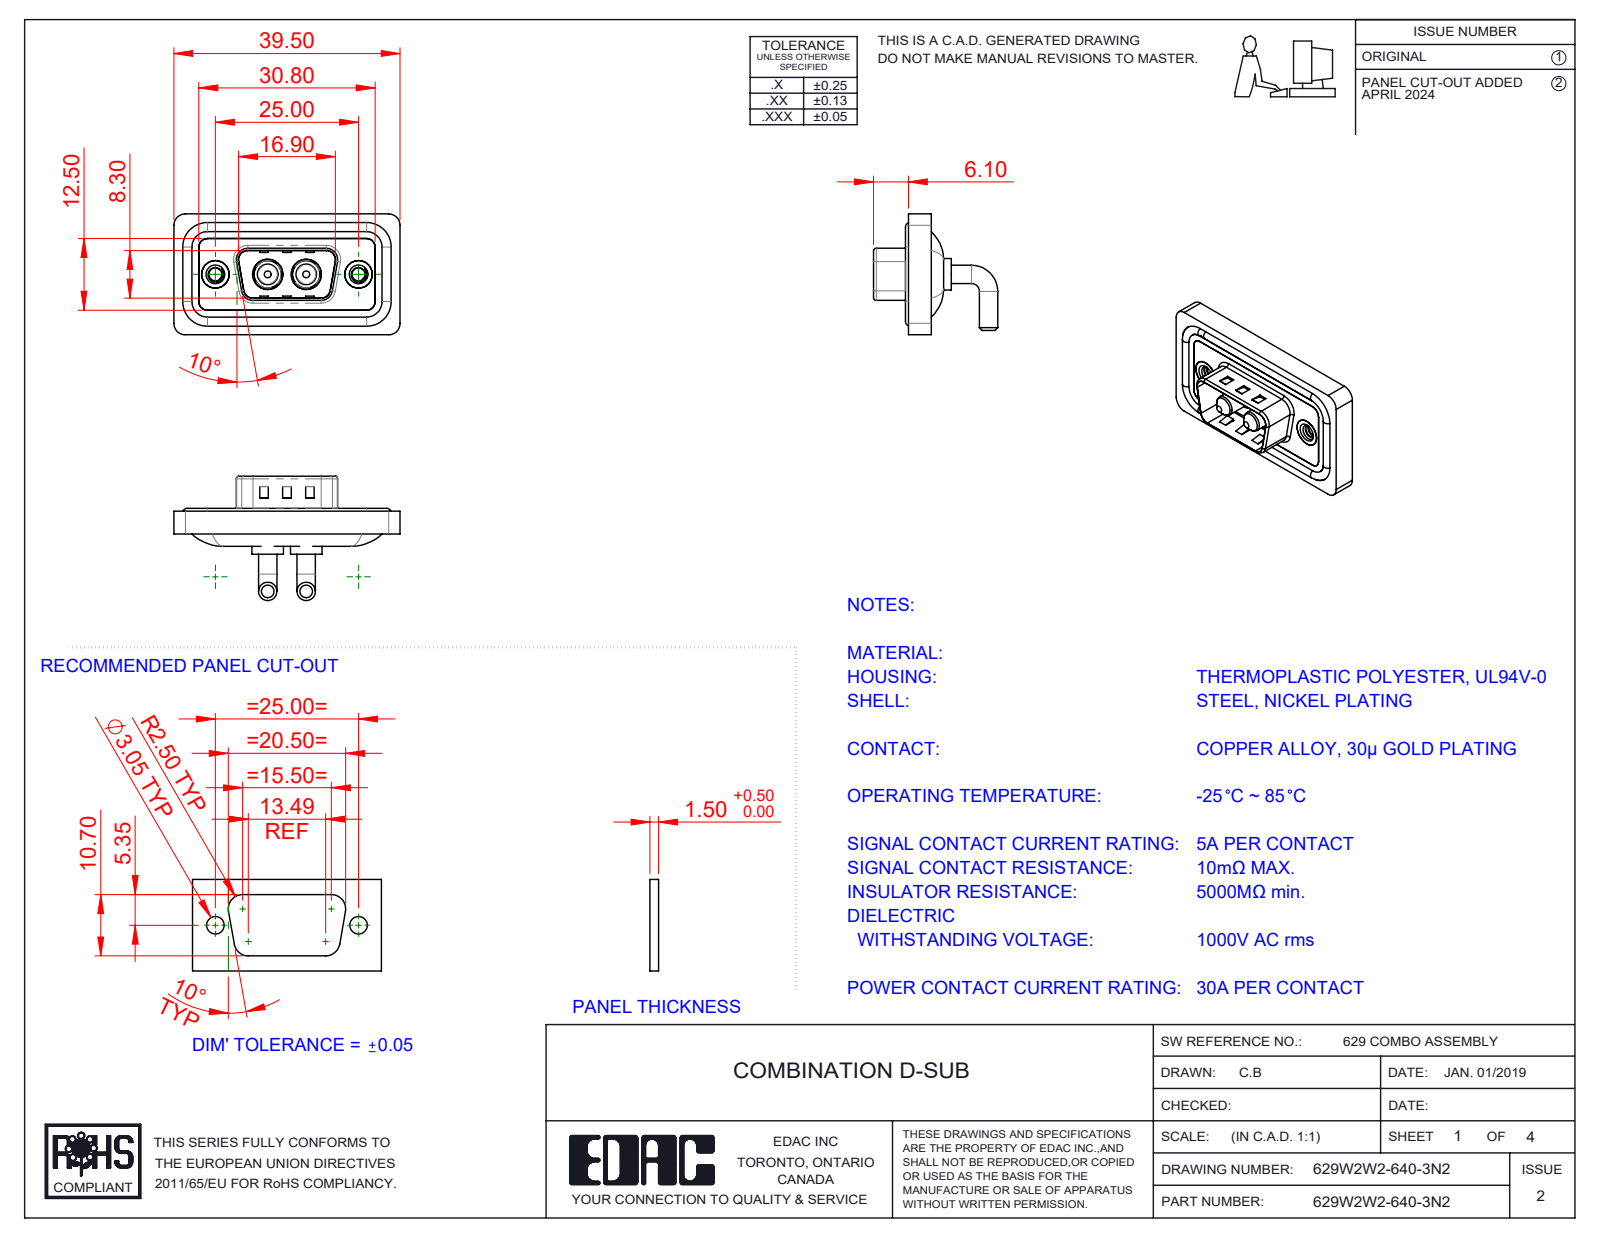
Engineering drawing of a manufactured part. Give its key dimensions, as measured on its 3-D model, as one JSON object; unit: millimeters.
{"part_name": "629Combo Shell Front_09 Contacts; 629Combo Threaded Rivet_2; 629Combo Waterproof Housing_09 Contacts; 629W2W2-640-3N2 (+3 more)", "step_written_by": "SolidWorks 2023 (CONFIG_CONTROL_DESIGN)", "units": "millimeters", "bodies": {"solids": 11, "faces": 497, "planar": 165, "cylindrical": 222, "other": 110}, "overall_size": [39.5, 21.7, 21.1], "volume_mm3": 4651, "surface_area_mm2": 7205, "round_holes": [[2.26, 2], [4, 2], [4.8, 2], [4.85, 2], [5, 2], [5.3, 2]], "round_bosses_or_shafts": [[3.2, 4], [1.6, 4], [5.5, 2], [5.2, 2], [4.9, 2], [4.75, 2], [3.75, 2], [3.6, 2]], "partial_cylinders_radius": [[1.5, 18], [2, 18], [0.5, 8], [1.6, 8], [0.25, 4], [0.6, 4], [0.65, 4], [0.9, 4]], "face_to_face_distances": [0.4, 2.9, 1.1, 0.8, 2.1, 2.5, 3.1, 1.6, 4.5, 1.5], "hole_center_spacings": [9.14, 15.86, 6.72, 25]}
